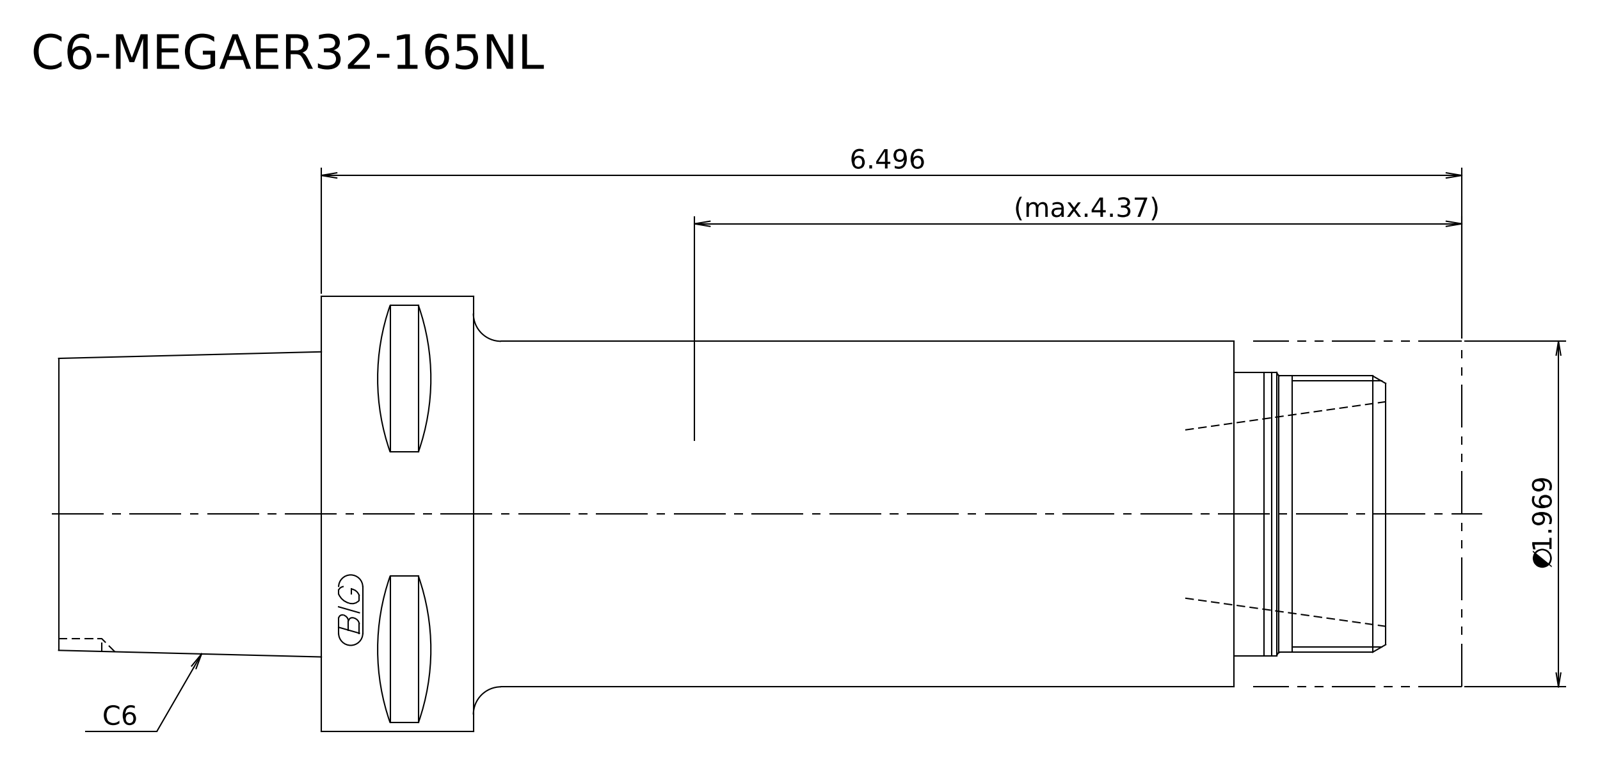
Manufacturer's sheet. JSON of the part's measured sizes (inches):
{"step_written_by": "Kubotek KeyCreator 2011 V10.0.2 (22737) (automotive_design)", "units": "inches", "bodies": {"solids": 2, "faces": 18, "planar": 7, "cylindrical": 5, "other": 6}, "overall_size": [7.992, 2.48, 2.48], "volume_in3": 26.11, "surface_area_in2": 68, "round_bosses_or_shafts": [[2.48, 1], [1.969, 1], [1.614, 1], [1.575, 1]], "face_to_face_distances": [1.189, 6.496, 5.307, 7.992, 6.803, 1.496, 0.433, 0.756, 6.063, 7.559]}
